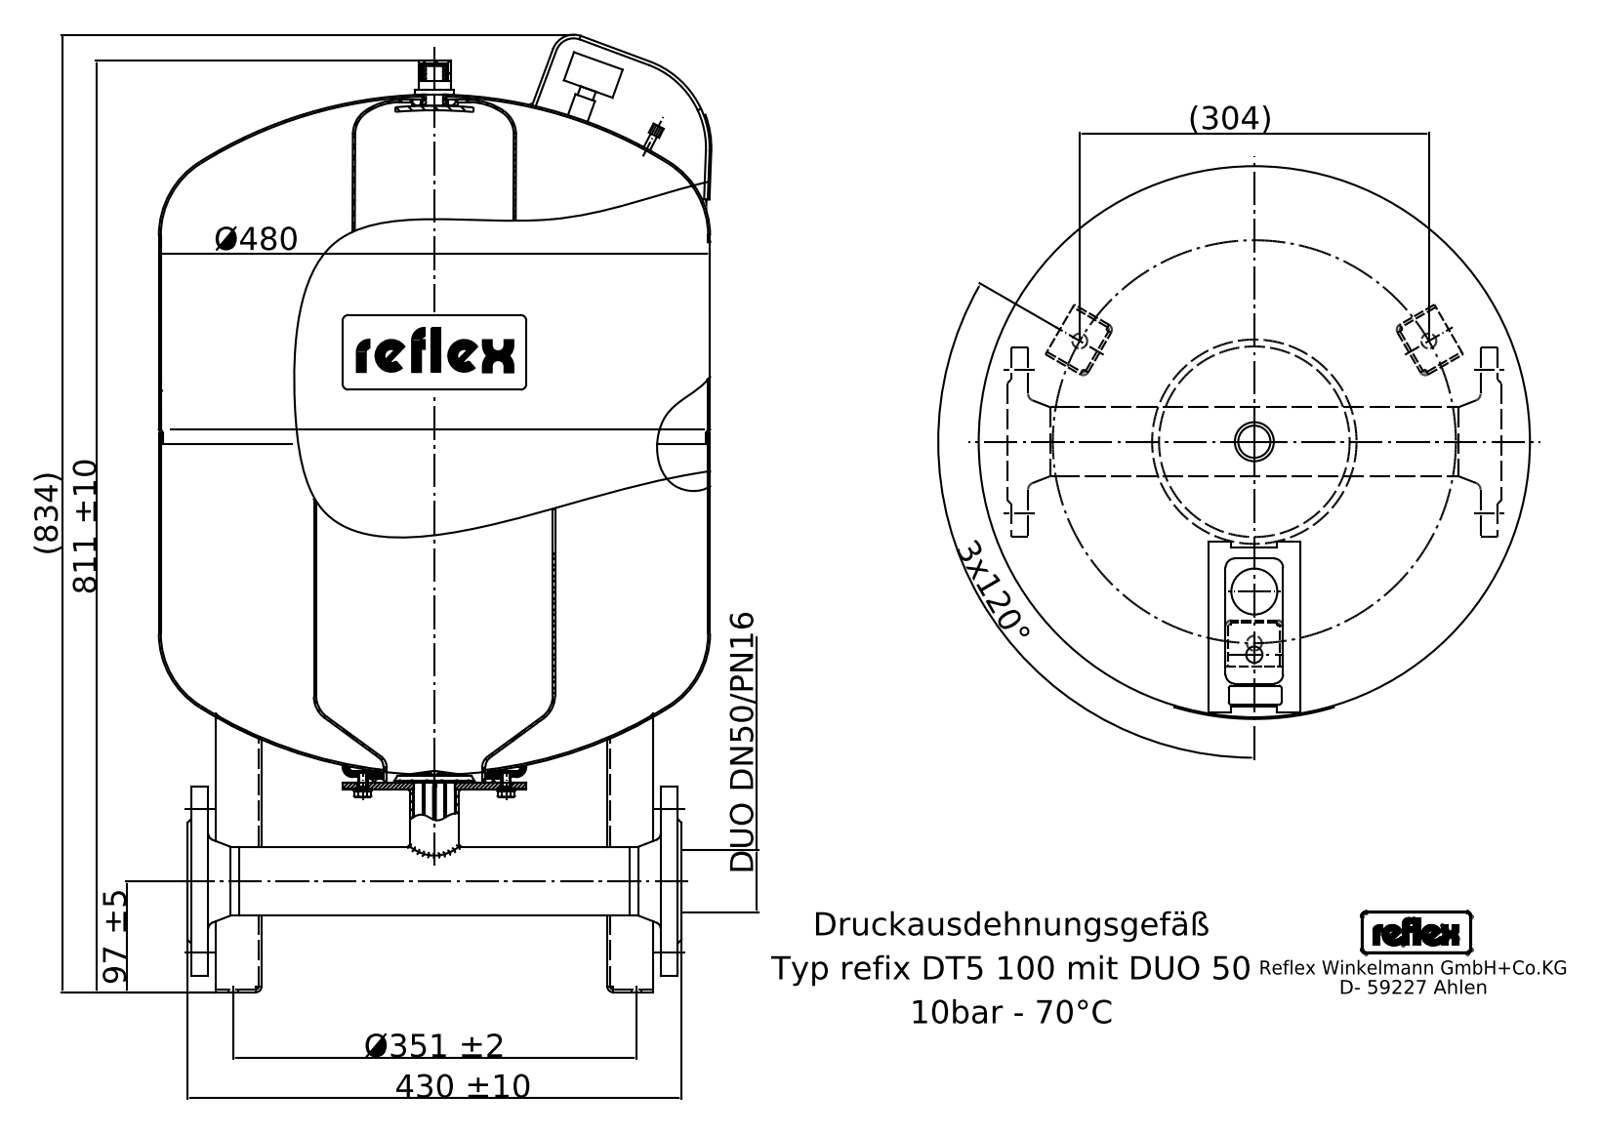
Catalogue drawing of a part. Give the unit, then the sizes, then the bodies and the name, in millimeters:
Units: millimetres
Overall size (bounding box): 828.24 × 480 × 480
Round holes (diameter × count): ⌀19 ×4, ⌀13.4 ×3, ⌀2.48 ×1, ⌀3.8 ×1, ⌀4.3 ×1, ⌀4.4 ×1, ⌀5.45 ×1, ⌀7 ×1, ⌀8 ×1, ⌀11.4 ×1, ⌀60.3 ×1, ⌀92 ×1
Round bosses / shafts (diameter × count): ⌀10 ×9, ⌀480 ×1, ⌀165 ×1, ⌀160 ×1, ⌀140 ×1, ⌀62 ×1, ⌀42.4 ×1, ⌀34 ×1
Partial cylindrical surfaces — rounded edges, fillets, slot ends (radius × count): R1 ×15, R2.5 ×15, R5 ×15, R3.94 ×4, R1.57 ×3, R2.69 ×2, R4.72 ×2, R6.49 ×2
Main face-to-face distances: 323, 2.5, 47.5, 50, 45, 141, 464, 6, 147, 470
Hole centre spacings: 62.49, 88.38, 175.5, 303.98, 124.99
Volume: 92 980 000 mm³ · Surface area: 2 299 000 mm²
Bodies: 23 solids, 533 faces (226 planar, 189 cylindrical, 118 other)
STEP written by: Mechanical Desktop 2008 (CONFIG_CONTROL_DESIGN)
